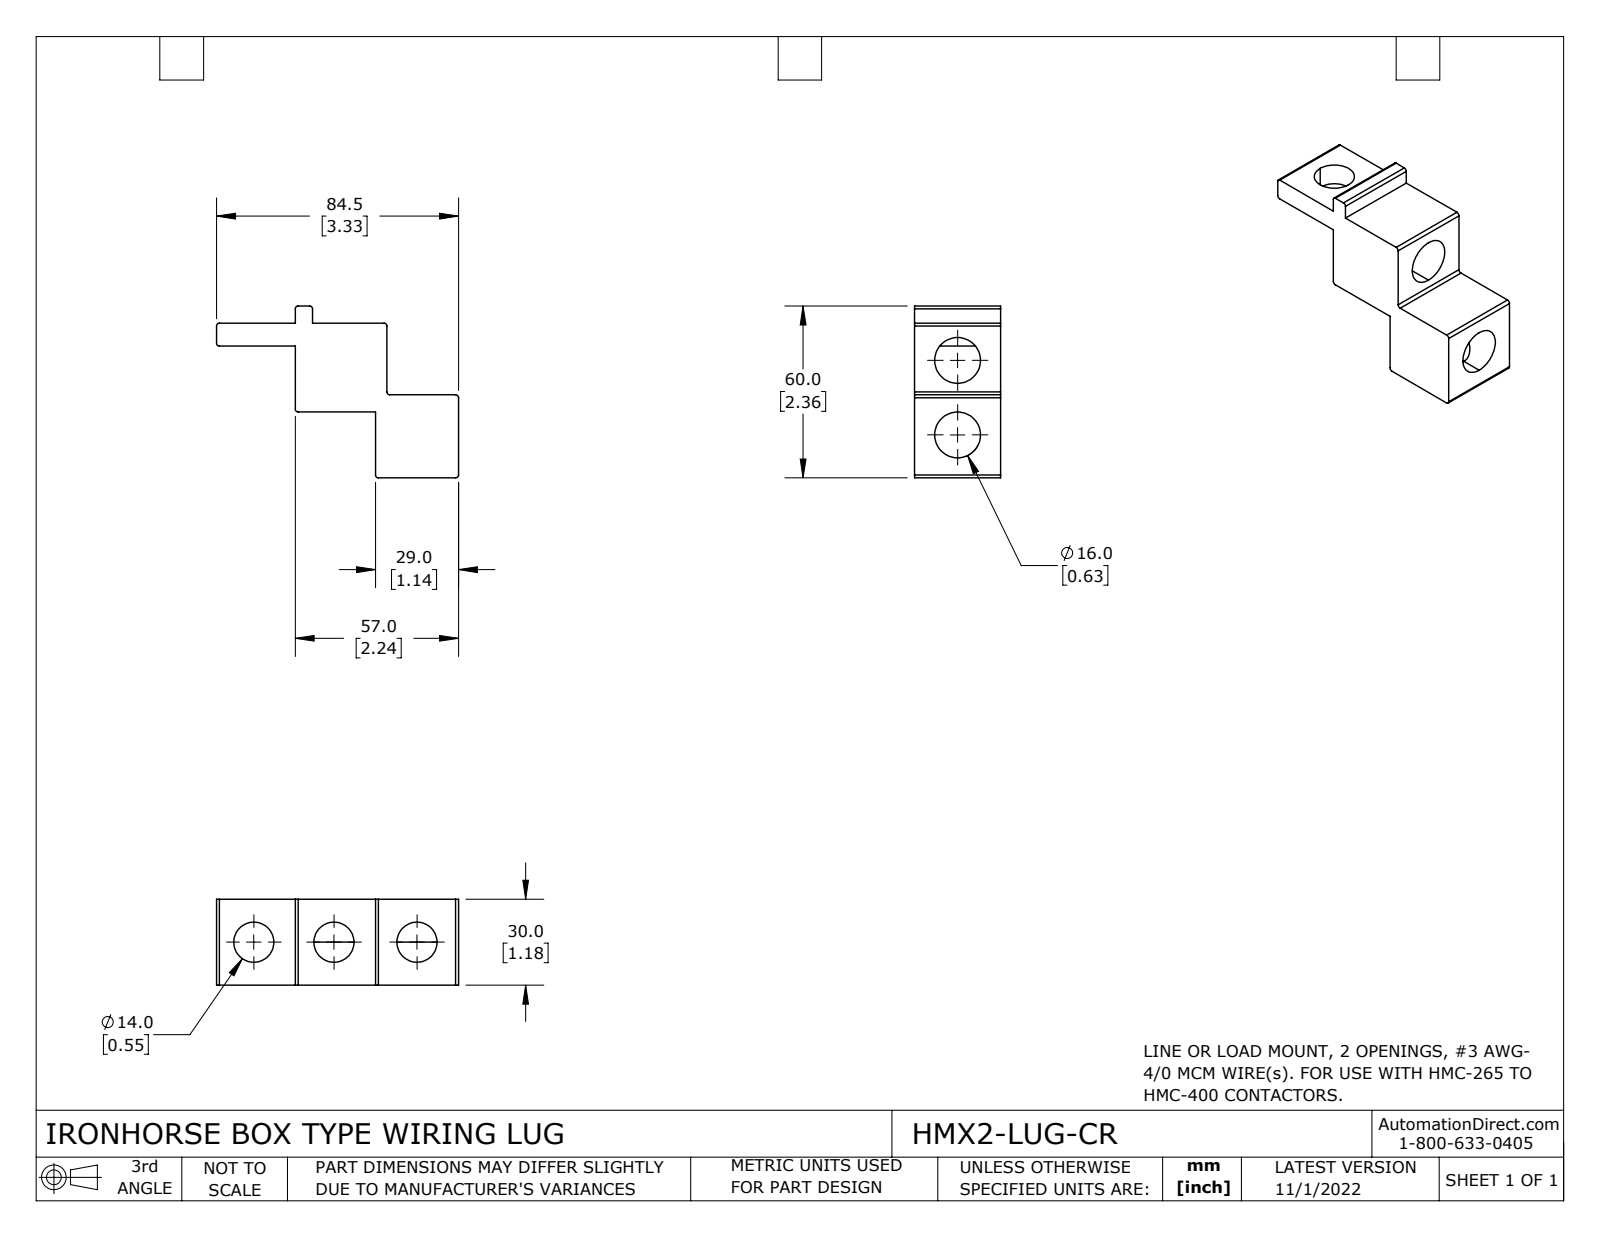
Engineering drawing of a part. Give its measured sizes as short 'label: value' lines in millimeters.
name: HMX2-LUG-CR
written by: SolidWorks 2021 (CONFIG_CONTROL_DESIGN)
unit: mm
bodies: 1 solid, 37 faces (17 planar, 20 cylindrical, 0 other)
size: 84.5 × 60 × 30
volume: 45 520 mm³; area: 15 280 mm²
holes: 3× ⌀14, 2× ⌀16
rounds: 10× R1
face distances: 30, 23, 25, 29, 6, 31, 54, 46, 17, 8
hole spacings: 26, 28, 29, 57
